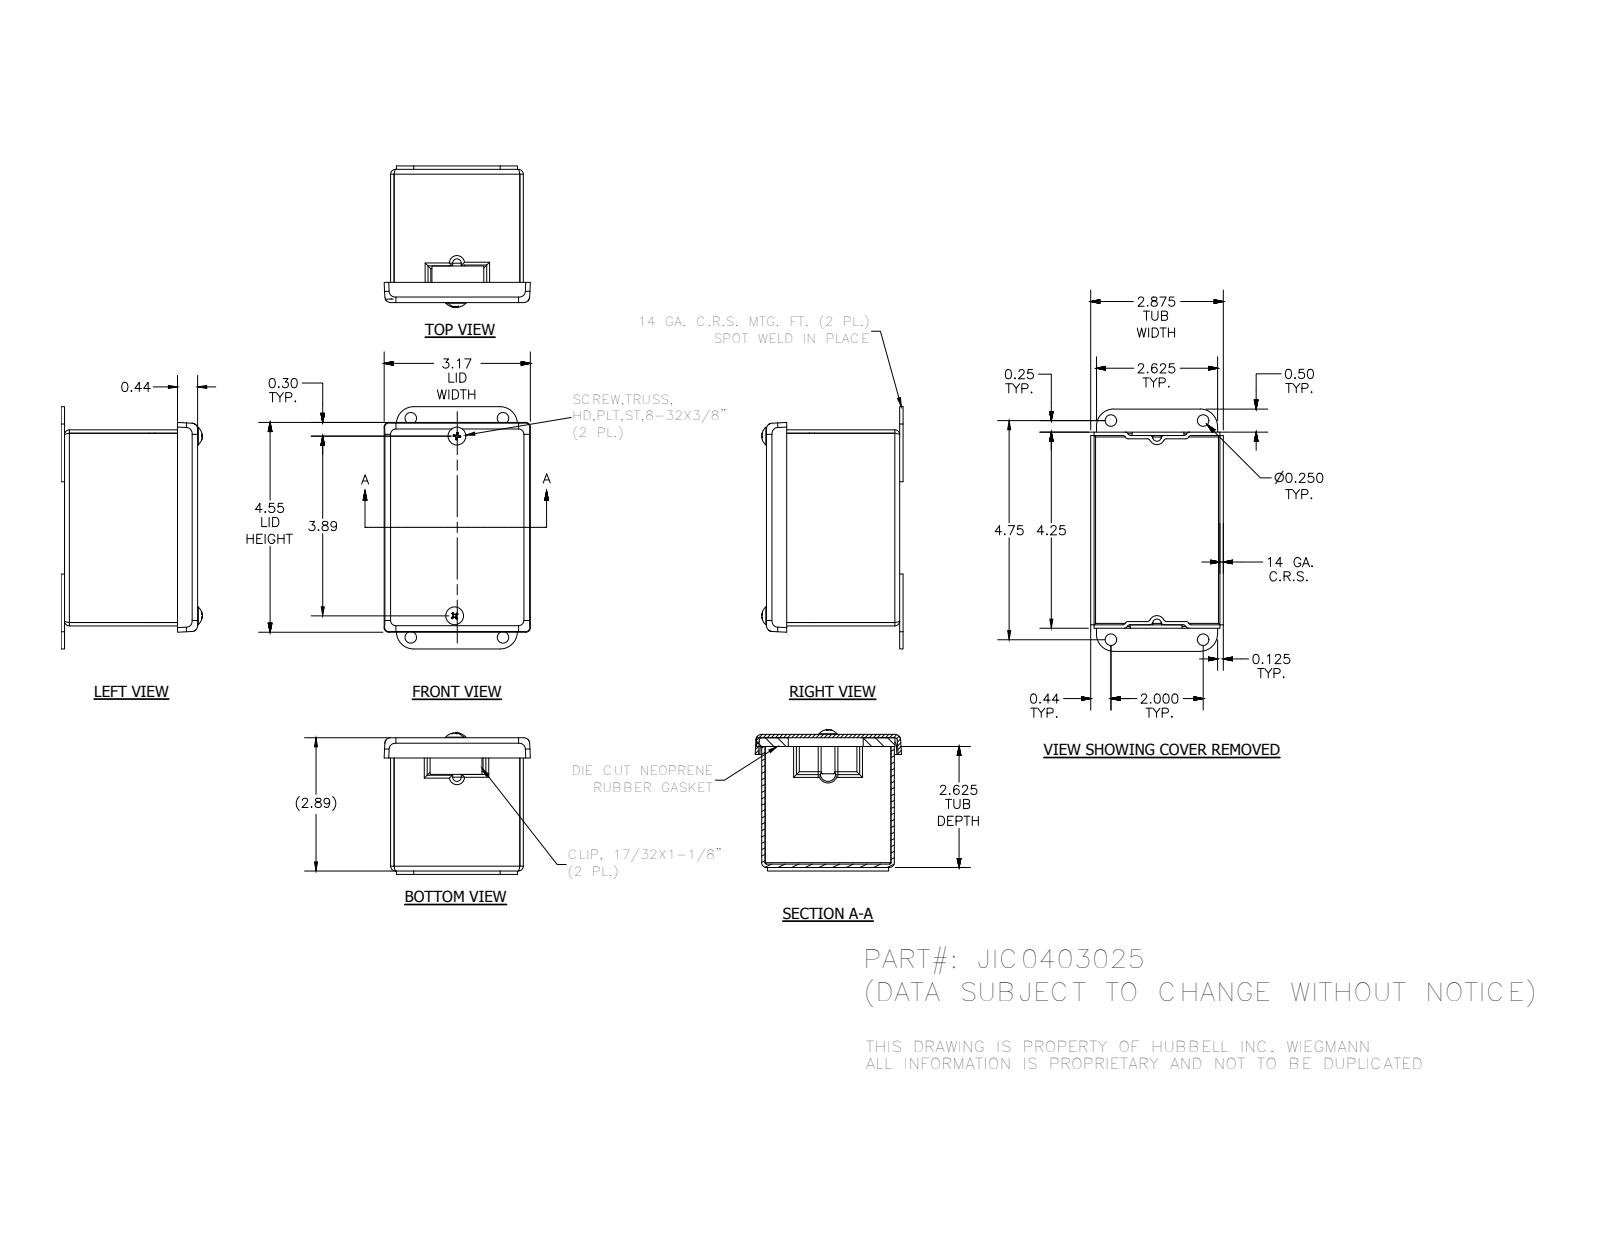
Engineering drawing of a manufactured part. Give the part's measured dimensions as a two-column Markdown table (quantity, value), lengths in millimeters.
| quantity | value |
| --- | --- |
| part name | BR4X3P; 31643; JIC4325P; 31811 (+3 more) |
| STEP written by | Autodesk Inventor 2014 (AUTOMOTIVE_DESIGN) |
| units | millimeters |
| bodies | 9 solids, 315 faces (117 planar, 92 cylindrical, 106 other) |
| overall size | 133.72 × 81.39 × 78.05 |
| volume | 116 868 mm³ |
| surface area | 114 976 mm² |
| round holes (diameter × count) | 6.35 × 4, 5.56 × 2 |
| round bosses / shafts (diameter × count) | 9.75 × 2, 4.17 × 2 |
| partial cylindrical surfaces (radius × count) | 1.8 × 38, 3.17 × 8, 2.54 × 6, 0.66 × 4, 0.79 × 4, 1.29 × 4, 2.39 × 4, 2.67 × 4 |
| main face-to-face distances | 1.88, 71.44, 71.15, 73.32, 106.08, 69.56, 69.27, 73.03, 6.64, 4.76 |
| hole center spacings | 112.8, 113.69, 27.22, 27.24, 27.57, 27.58, 50.79, 50.8 |
